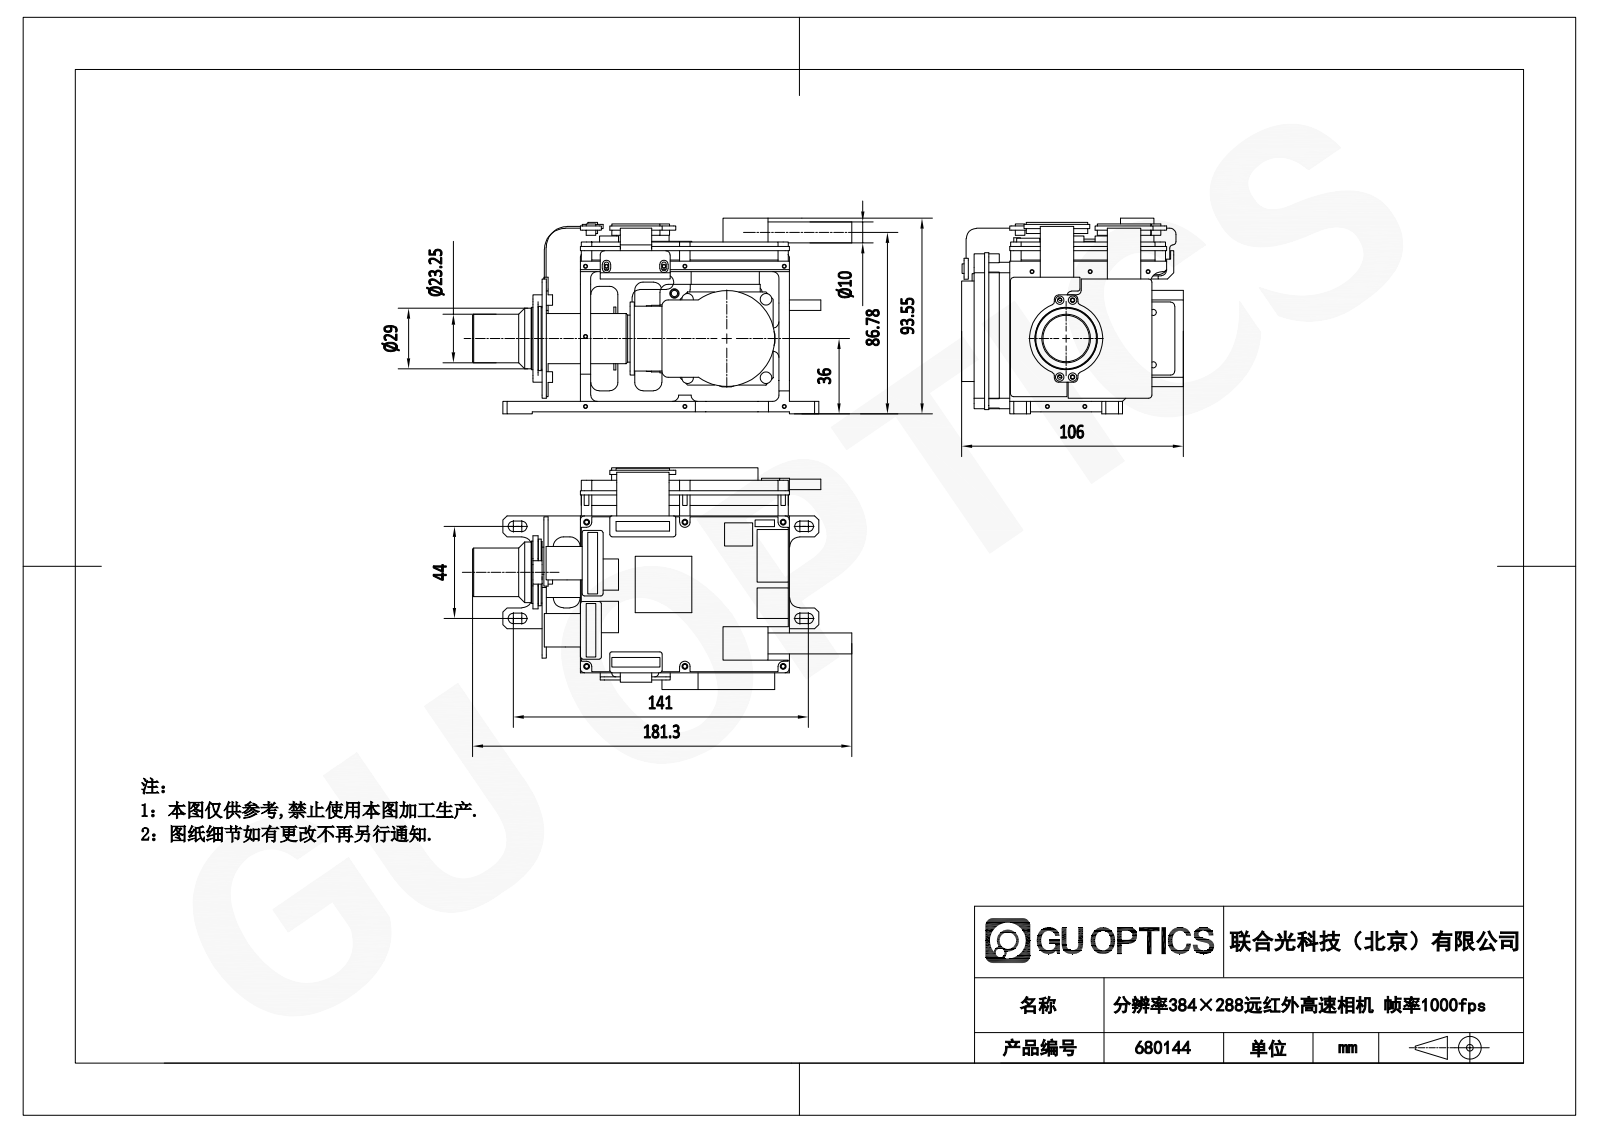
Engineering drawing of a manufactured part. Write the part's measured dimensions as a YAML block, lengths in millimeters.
part_name: "680144"
step_written_by: "SolidWorks 2020 (CONFIG_CONTROL_DESIGN)"
units: millimeters
bodies: {solids: 0, faces: 1157, planar: 688, cylindrical: 347, other: 122}
overall_size: [181.3, 106, 93.55]
round_holes:
  - {diameter: 1.5, count: 18}
  - {diameter: 2.05, count: 16}
  - {diameter: 2.8, count: 12}
  - {diameter: 5, count: 12}
  - {diameter: 2.2, count: 6}
  - {diameter: 3, count: 5}
  - {diameter: 1.75, count: 4}
  - {diameter: 4.5, count: 3}
  - {diameter: 3.09, count: 2}
  - {diameter: 3.07, count: 1}
  - {diameter: 3.08, count: 1}
  - {diameter: 27.76, count: 1}
round_bosses_or_shafts:
  - {diameter: 2.5, count: 6}
  - {diameter: 2, count: 6}
  - {diameter: 6.6, count: 4}
  - {diameter: 5.6, count: 4}
  - {diameter: 46, count: 1}
  - {diameter: 31.85, count: 1}
  - {diameter: 29.8, count: 1}
  - {diameter: 29.44, count: 1}
partial_cylinders:
  - {radius: 5, count: 38}
  - {radius: 2, count: 29}
  - {radius: 1, count: 26}
  - {radius: 1.5, count: 22}
  - {radius: 2.5, count: 21}
  - {radius: 3, count: 21}
  - {radius: 4, count: 17}
  - {radius: 1.1, count: 4}
face_to_face_distances: [5, 2, 0.5, 9, 34, 72, 7, 67, 6, 16]
hole_center_spacings: [47, 47.5, 6.2, 18.66, 45.19, 65, 80.21, 82.13]
